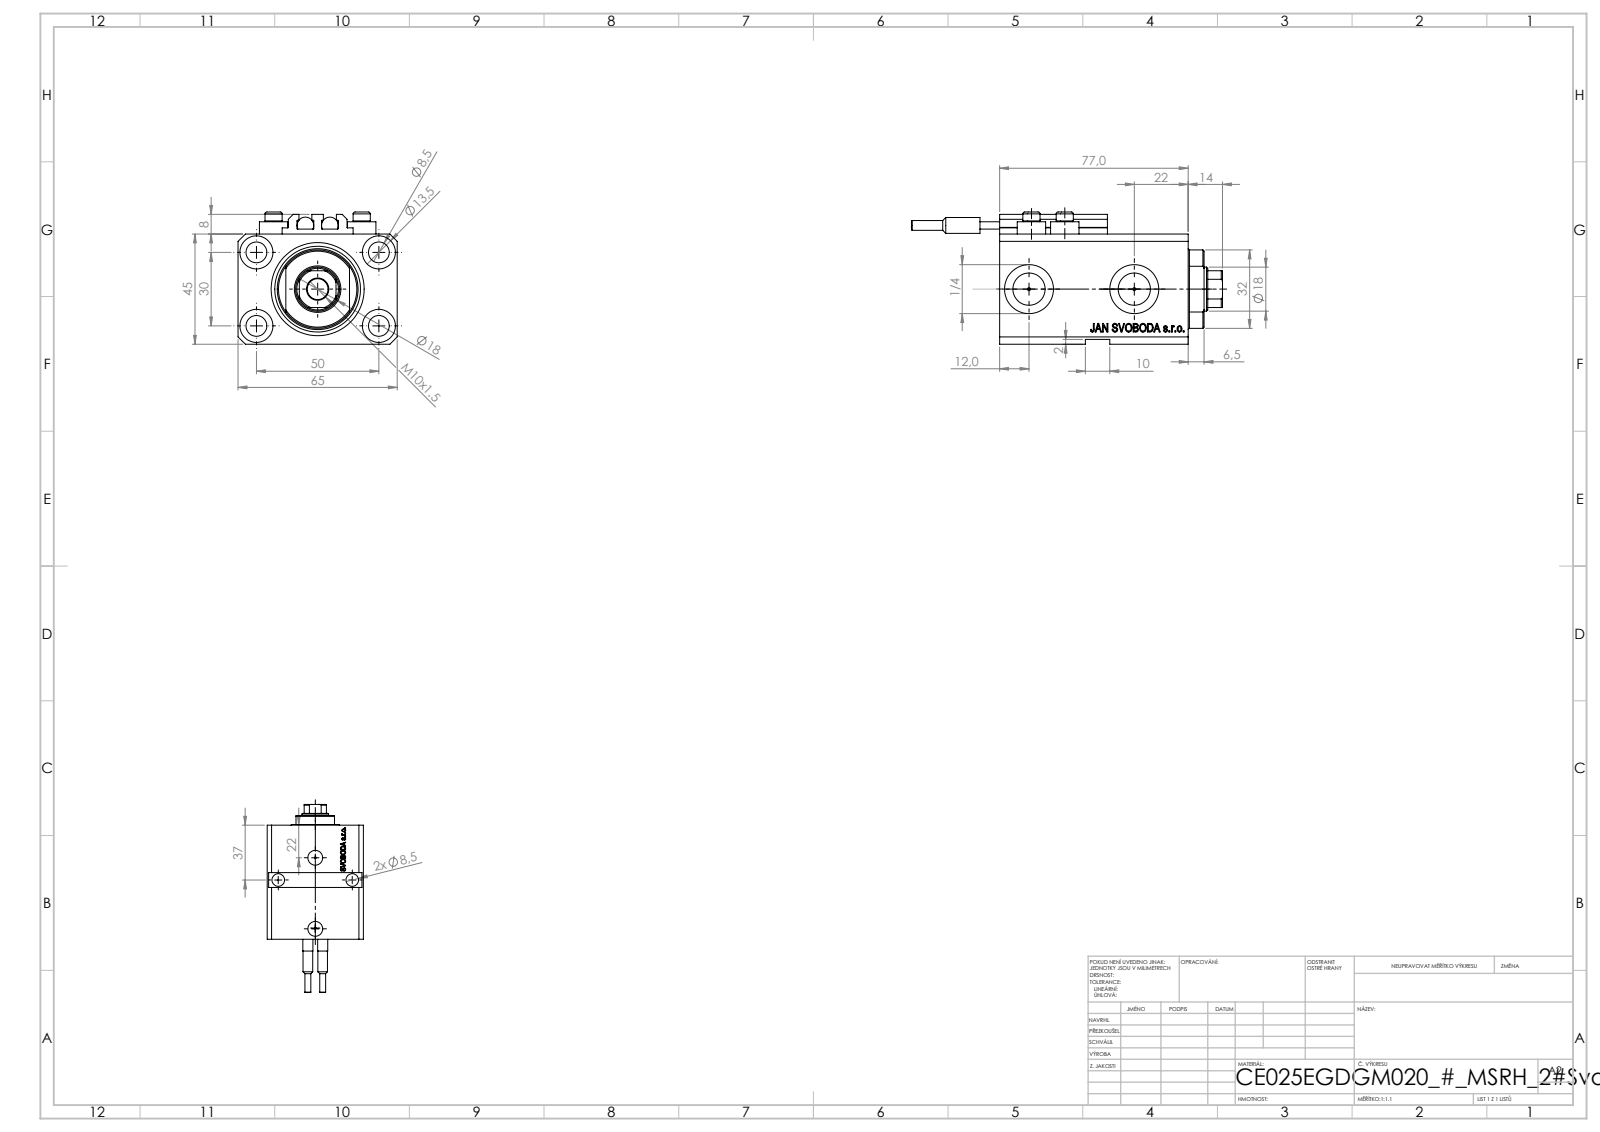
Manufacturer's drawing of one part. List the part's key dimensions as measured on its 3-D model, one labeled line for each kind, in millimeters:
Part name (STEP PRODUCT): ALLEN BOLT V250CE; V250CE_C_VCP; SWITCH_V250CE; V250CE_E_Body (+1 more)
STEP written by: SolidWorks 2019 (CONFIG_CONTROL_DESIGN)
Units: millimetres
Bodies: 10 solids, 1135 faces (547 planar, 150 cylindrical, 438 other)
Overall size (bounding box): 127 × 65 × 54
Volume: 199 731 mm³ · Surface area: 63 072 mm²
Round holes (diameter × count): ⌀8.5 ×7, ⌀1.25 ×4, ⌀4 ×4, ⌀13.5 ×4, ⌀10 ×2, ⌀13.16 ×2, ⌀20 ×2, ⌀18 ×1, ⌀25 ×1, ⌀38 ×1
Round bosses / shafts (diameter × count): ⌀11.6 ×4, ⌀7 ×4, ⌀6.8 ×2, ⌀6.5 ×2, ⌀4 ×2
Partial cylindrical surfaces — rounded edges, fillets, slot ends (radius × count): R0.2 ×10, R8.5 ×1, R16 ×1
Main face-to-face distances: 45, 65, 63, 2, 14, 3, 77, 47, 5, 6.9
Hole centre spacings: 29.15, 50, 13.6, 15.12, 18.81, 18.97, 26.22, 26.61
